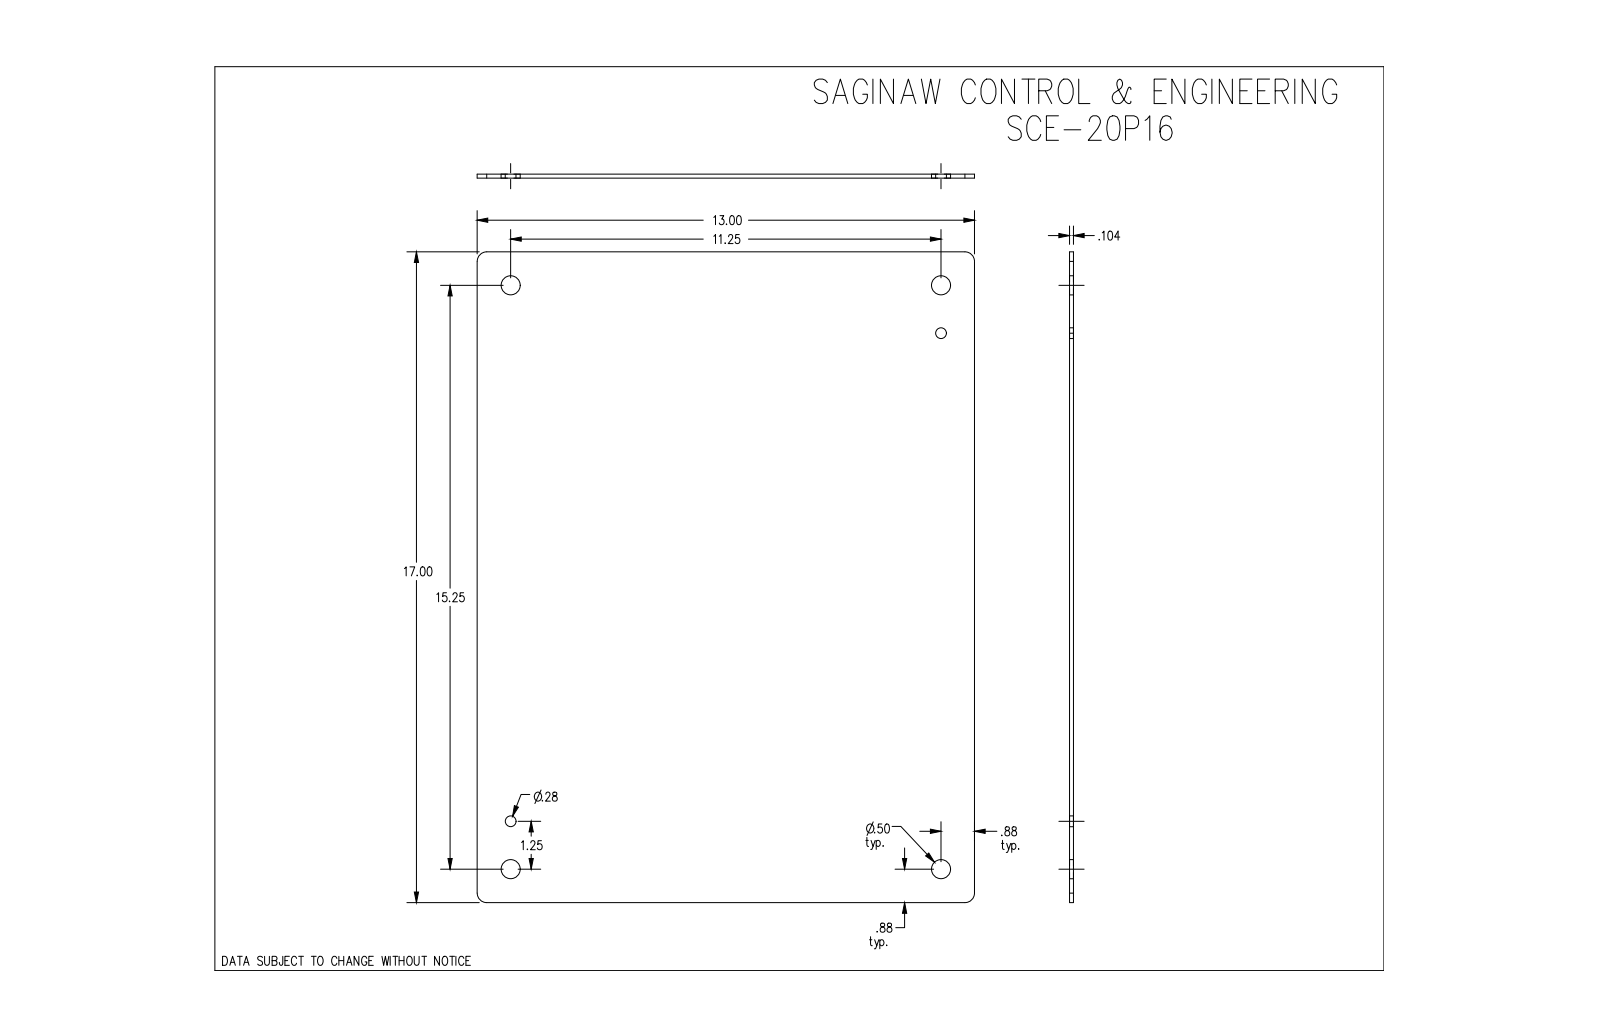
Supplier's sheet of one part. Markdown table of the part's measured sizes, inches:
| quantity | value |
| --- | --- |
| part name | SCE-20P16 |
| STEP written by | SolidWorks 2019 (CONFIG_CONTROL_DESIGN) |
| units | inches |
| bodies | 1 solid, 16 faces (6 planar, 10 cylindrical, 0 other) |
| overall size | 17 × 13 × 0.104 |
| volume | 22.88 in³ |
| surface area | 447.1 in² |
| round holes (diameter × count) | 0.5 × 4, 0.281 × 1, 0.281 × 1 |
| partial cylindrical surfaces (radius × count) | 0.25 × 4 |
| main face-to-face distances | 0.104, 13, 17 |
| hole center spacings | 1.25, 11.25, 11.32, 14, 15.25, 17.96, 18.95, 17.004 |
